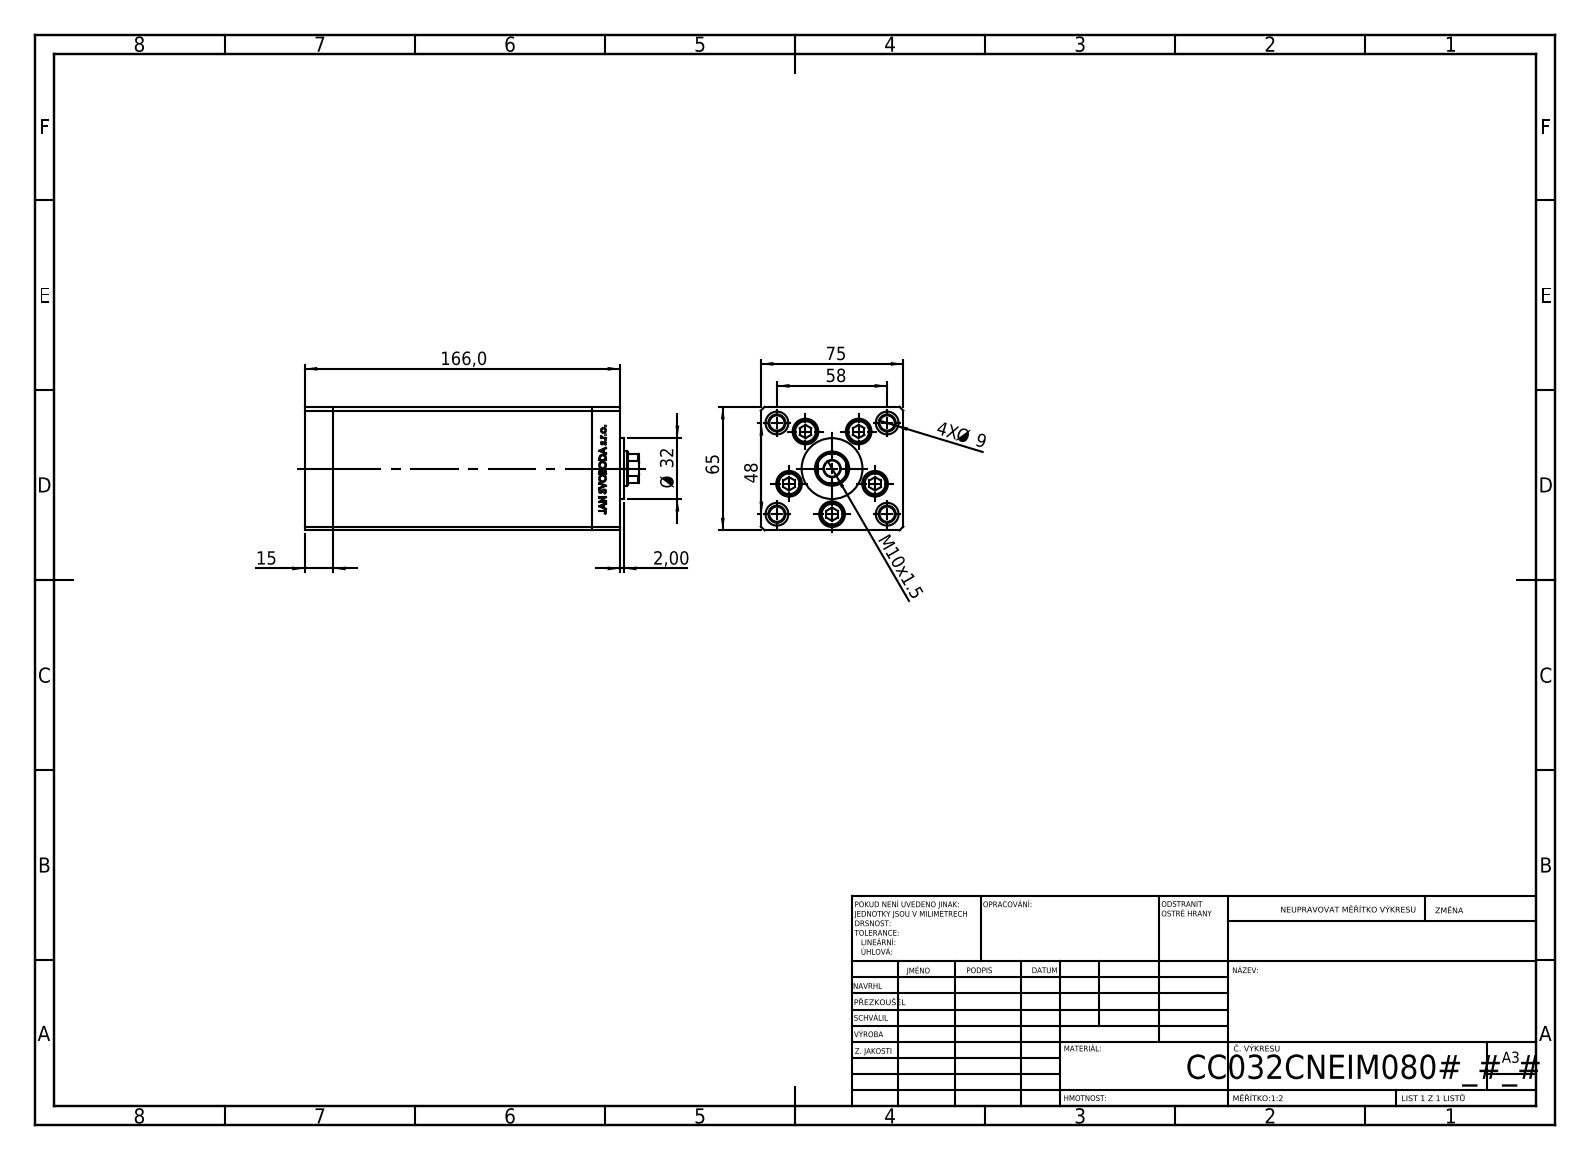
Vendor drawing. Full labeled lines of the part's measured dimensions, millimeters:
Part name (STEP PRODUCT): V220C_VC_C; V220C BACK_C; V220C_C MIDDLE; V220C FRONT (+1 more)
STEP written by: SolidWorks 2019 (CONFIG_CONTROL_DESIGN)
Units: millimetres
Bodies: 13 solids, 1159 faces (538 planar, 159 cylindrical, 462 other)
Overall size (bounding box): 176 × 75 × 65
Volume: 684 102 mm³ · Surface area: 141 321 mm²
Round holes (diameter × count): ⌀9 ×9, ⌀13.5 ×5, ⌀8 ×4, ⌀12 ×4, ⌀8.5 ×1, ⌀12.5 ×1, ⌀18 ×1
Round bosses / shafts (diameter × count): ⌀8 ×5, ⌀12.5 ×4, ⌀32 ×1
Partial cylindrical surfaces — rounded edges, fillets, slot ends (radius × count): R0.93 ×2, R8.5 ×1
Main face-to-face distances: 75, 65, 15, 136, 151, 166, 28, 142, 9, 54.5
Hole centre spacings: 24, 37.64, 15.67, 17.22, 27.71, 28.83, 29, 32.63
